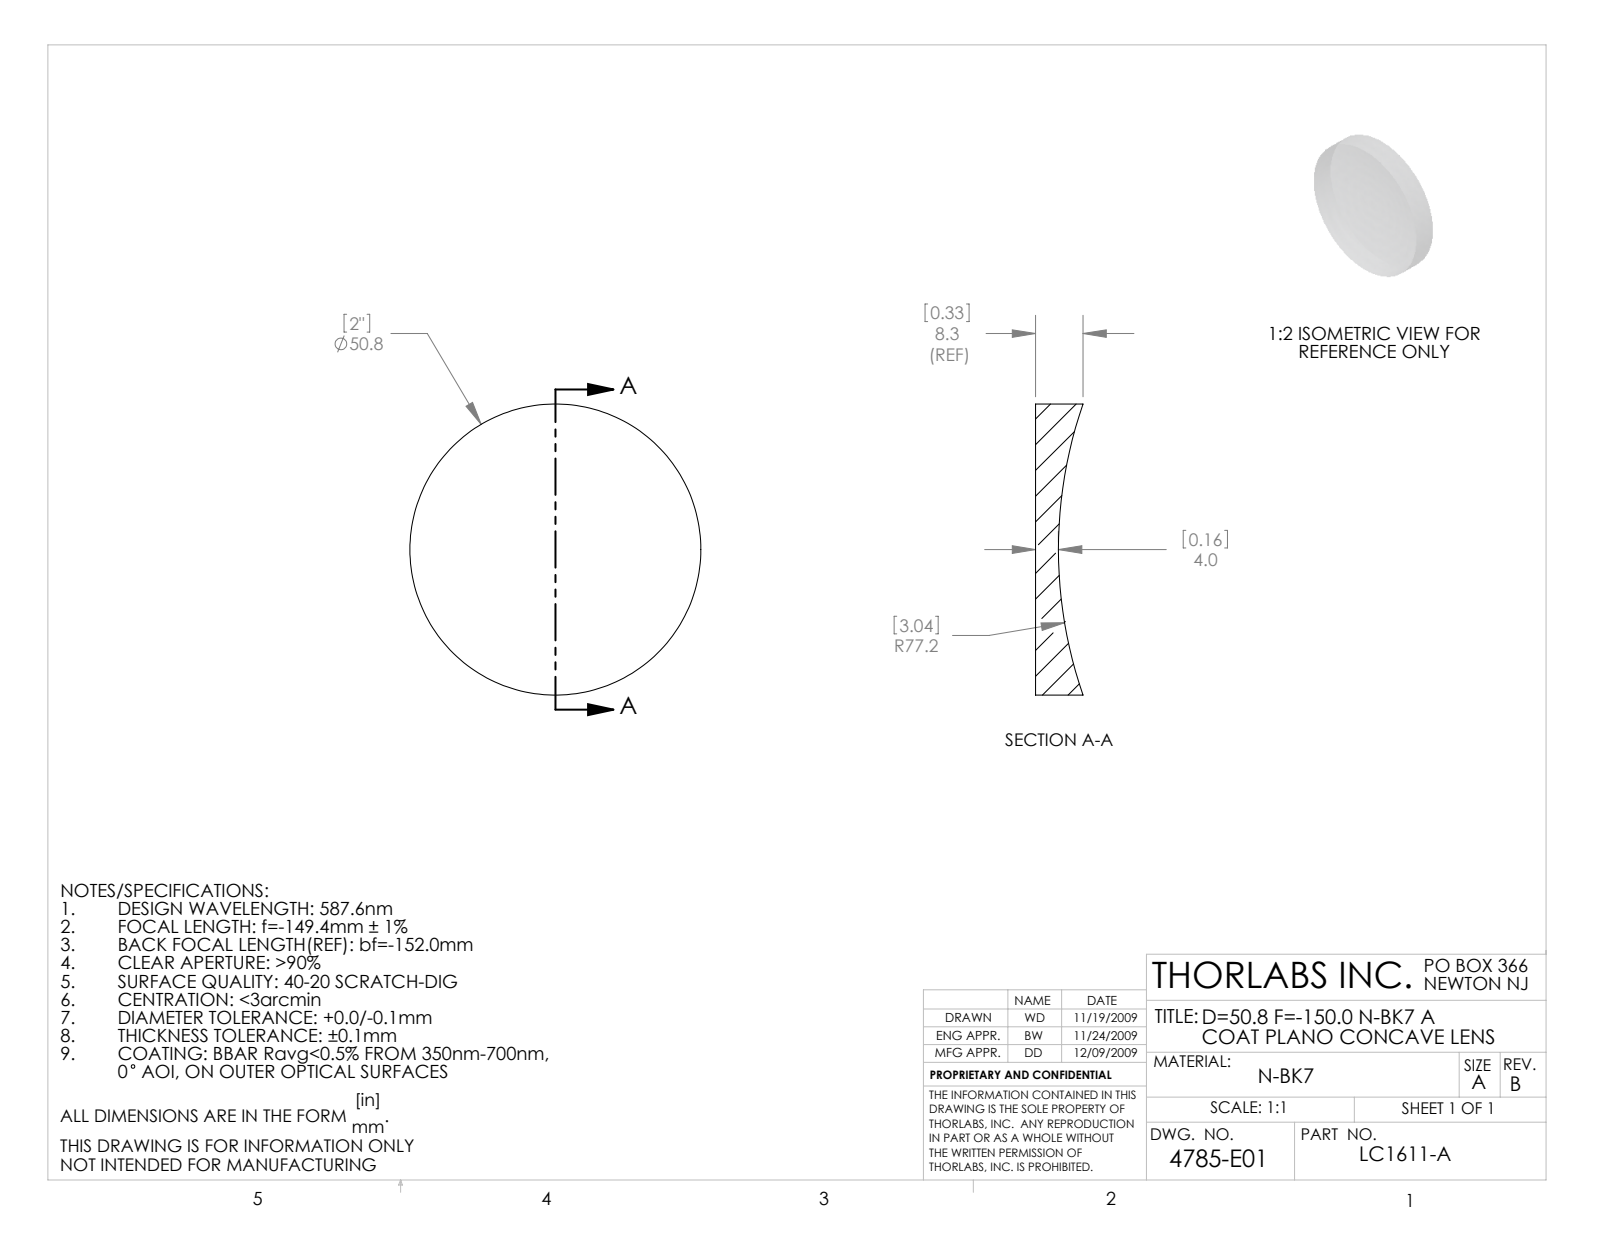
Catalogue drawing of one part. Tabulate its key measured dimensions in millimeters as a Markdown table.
| quantity | value |
| --- | --- |
| part name | 4785-E0W |
| STEP written by | SolidWorks 2009 (AUTOMOTIVE_DESIGN) |
| units | millimeters |
| bodies | 1 solid, 5 faces (1 planar, 2 cylindrical, 2 other) |
| overall size | 50.8 × 50.8 × 8.3 |
| volume | 12 422 mm³ |
| surface area | 5 436 mm² |
| round bosses / shafts (diameter × count) | 50.8 × 1 |
